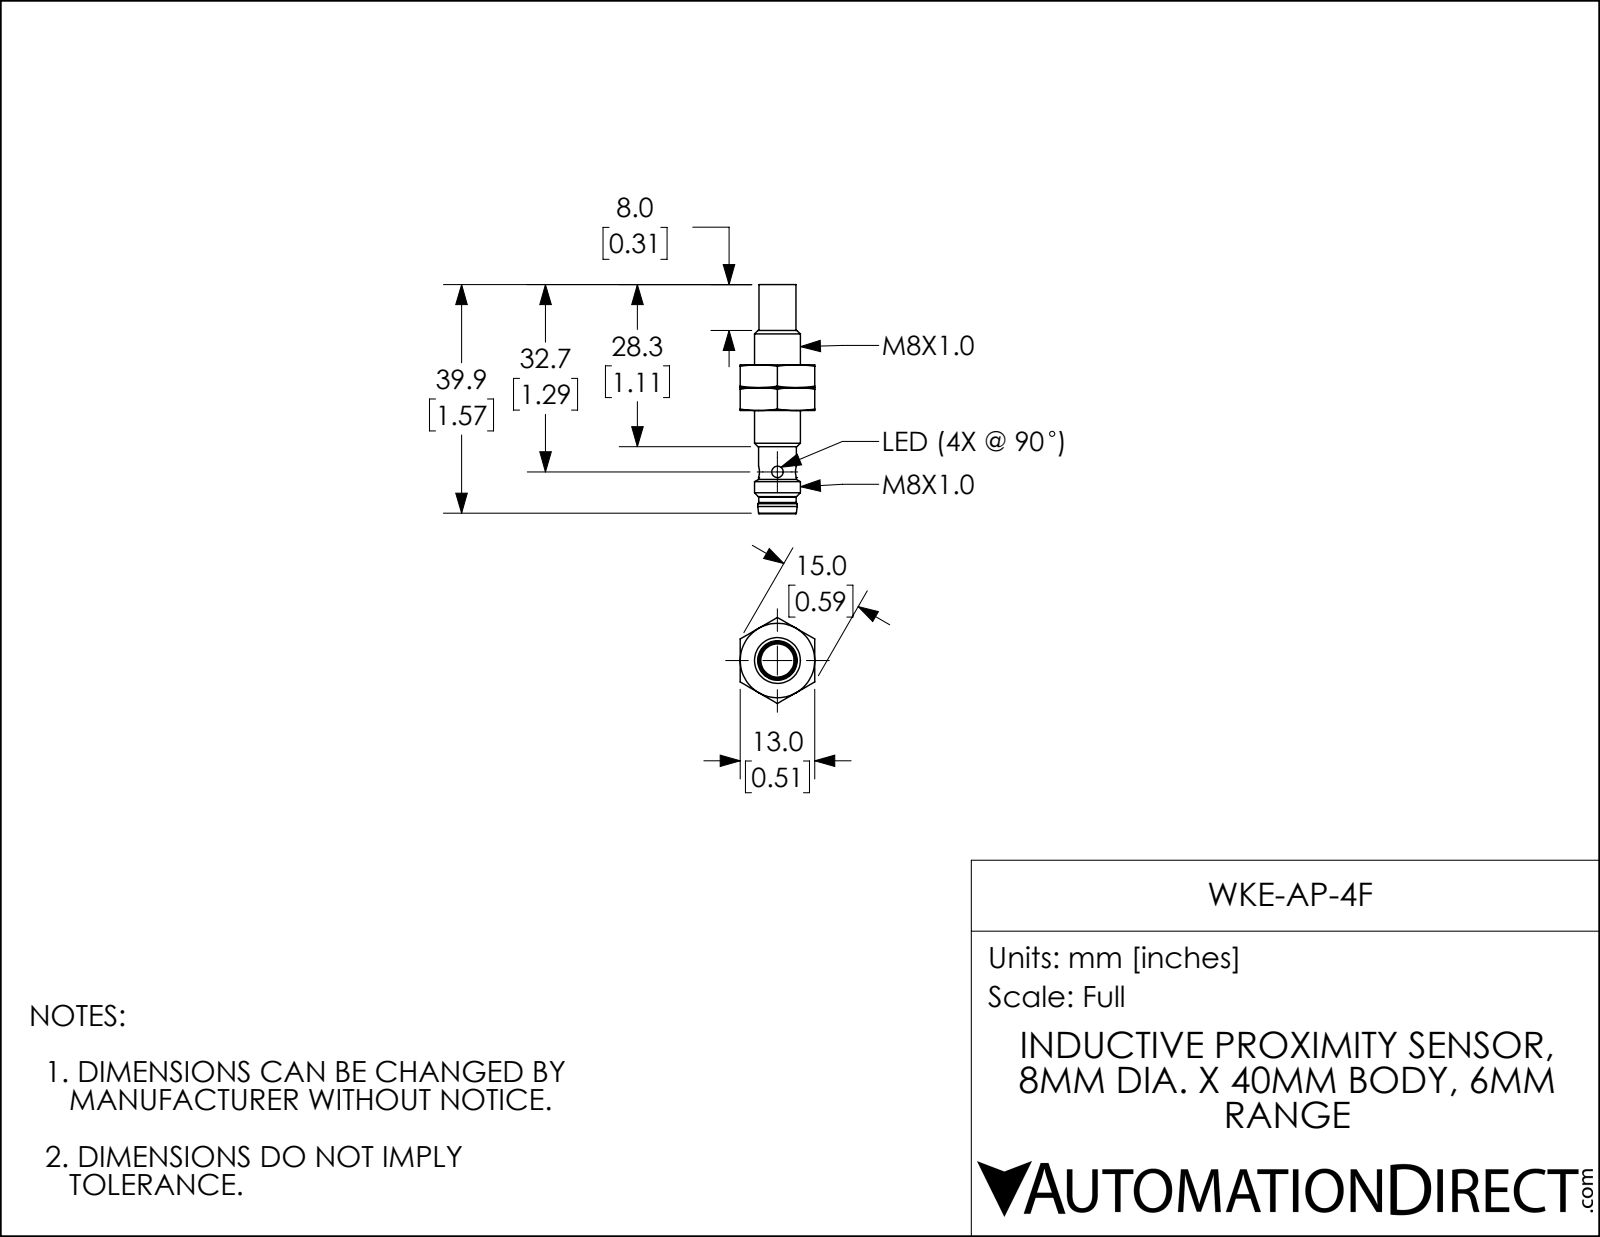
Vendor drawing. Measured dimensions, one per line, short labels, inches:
name: WKE-AP-4F
written by: SolidWorks 2017 (AUTOMOTIVE_DESIGN)
unit: in
bodies: 3 solids, 77 faces (22 planar, 18 cylindrical, 37 other)
size: 1.575 × 0.591 × 0.512
volume: 0.148 in³; area: 3.187 in²
holes: 2× ⌀0.079, 1× ⌀0.228, 1× ⌀0.272
bosses: 1× ⌀0.315, 1× ⌀0.272, 1× ⌀0.26, 1× ⌀0.256, 1× ⌀0.254, 1× ⌀0.25
rounds: 1× R0.115
face distances: 0.512, 0.157, 0.315, 0.551, 0.709, 0.866, 0.51, 0.667, 0.825, 1.376
